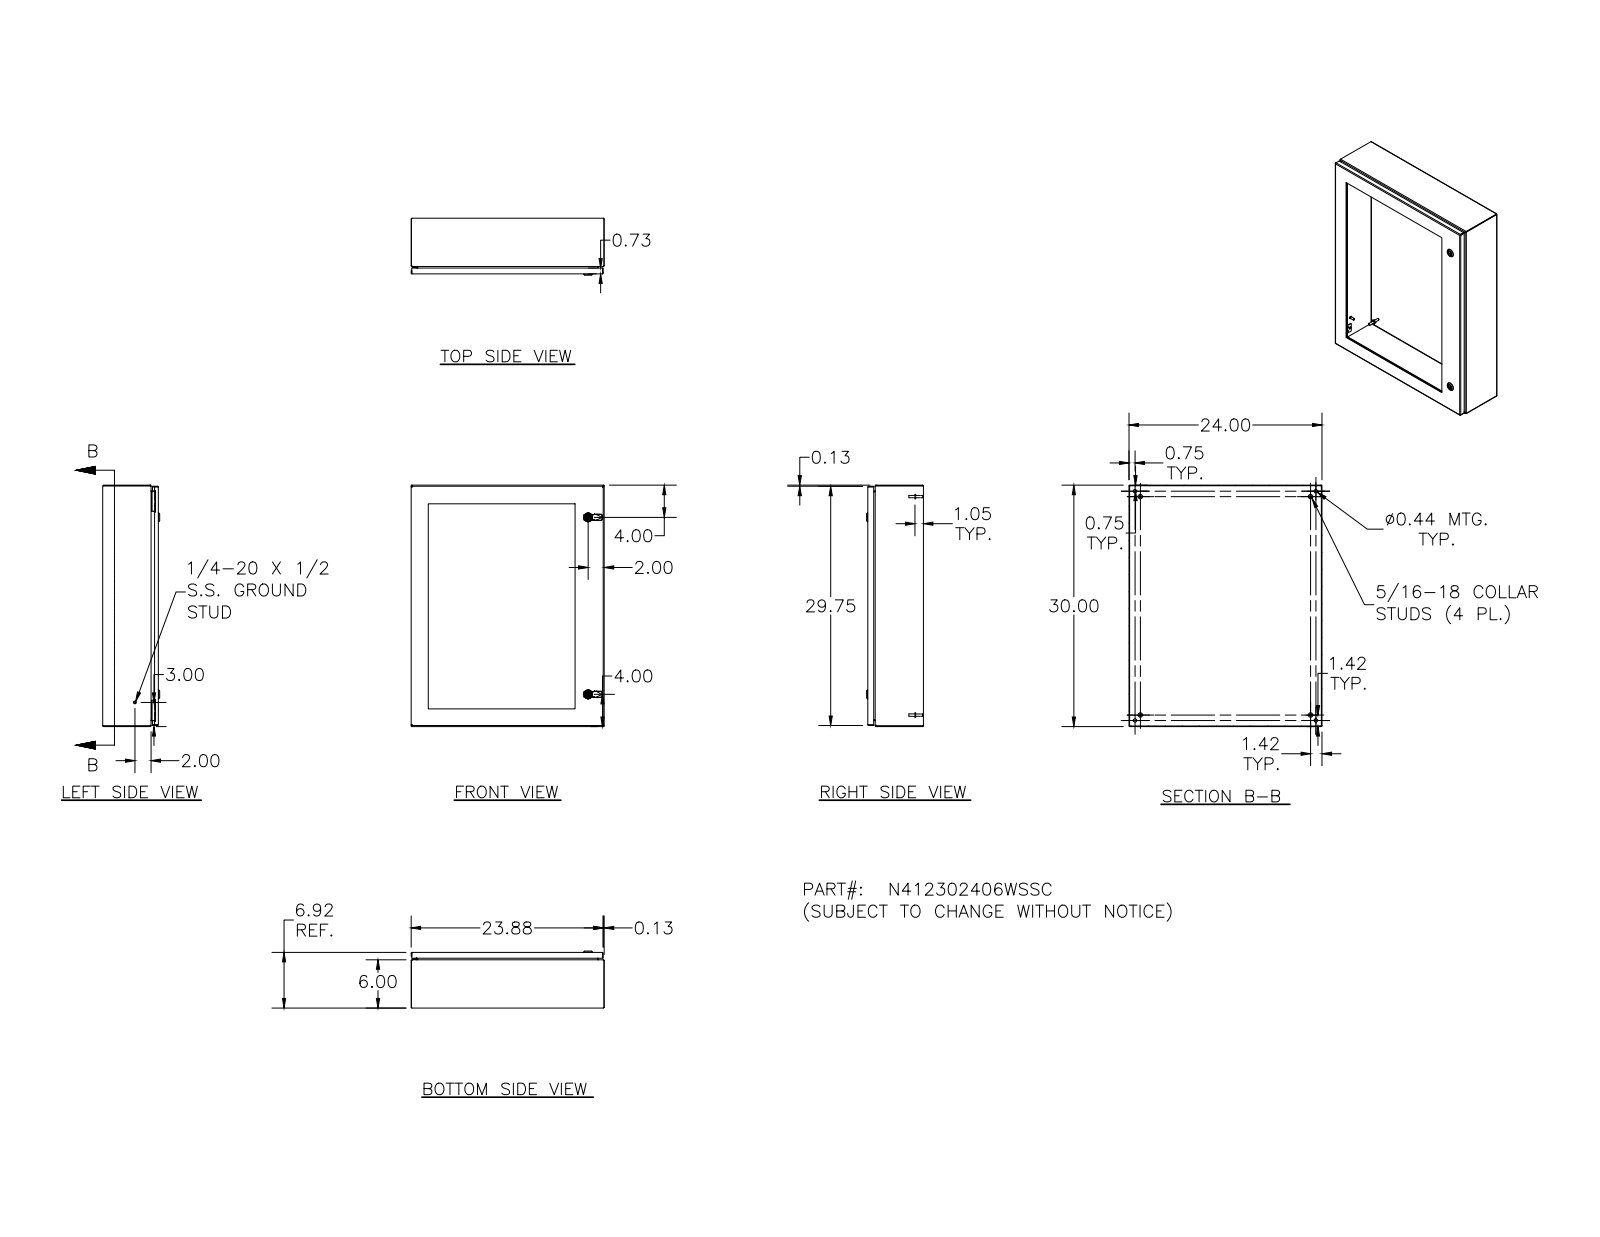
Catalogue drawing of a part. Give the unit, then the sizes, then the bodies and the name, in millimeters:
Units: millimetres
Overall size (bounding box): 762 × 609.6 × 179.7
Round holes (diameter × count): ⌀4 ×26, ⌀7.1 ×24, ⌀2.4 ×4, ⌀3.9 ×4, ⌀4.2 ×4, ⌀4.4 ×4, ⌀4.8 ×4, ⌀11.1 ×4, ⌀5 ×2, ⌀8 ×2, ⌀10 ×2, ⌀10.2 ×2
Round bosses / shafts (diameter × count): ⌀4.8 ×24, ⌀6.4 ×23, ⌀6.4 ×10, ⌀14.3 ×4, ⌀9.1 ×4, ⌀8.1 ×4, ⌀7.6 ×4, ⌀7 ×4
Partial cylindrical surfaces — rounded edges, fillets, slot ends (radius × count): R0.8 ×34, R1.3 ×26, R2.7 ×24, R0.4 ×18, R3.2 ×16, R0.5 ×15, R0.8 ×8, R4 ×8
Main face-to-face distances: 1.9, 173.8, 171.9, 6.4, 167.5, 165.6, 607.7, 760.1, 175.7, 8.2
Hole centre spacings: 101.6, 203.2, 304.8, 687, 660.4, 709.2, 406.4, 679.5
Volume: 4 456 000 mm³ · Surface area: 3 216 000 mm²
Bodies: 94 solids, 2494 faces (1017 planar, 688 cylindrical, 789 other)
Part name (STEP PRODUCT): N412302406WSSC; N412302406WSSCBKP; N4123024WSSCLID; HFW328176 (+8 more)
STEP written by: Autodesk Inventor 2011 (AUTOMOTIVE_DESIGN)
